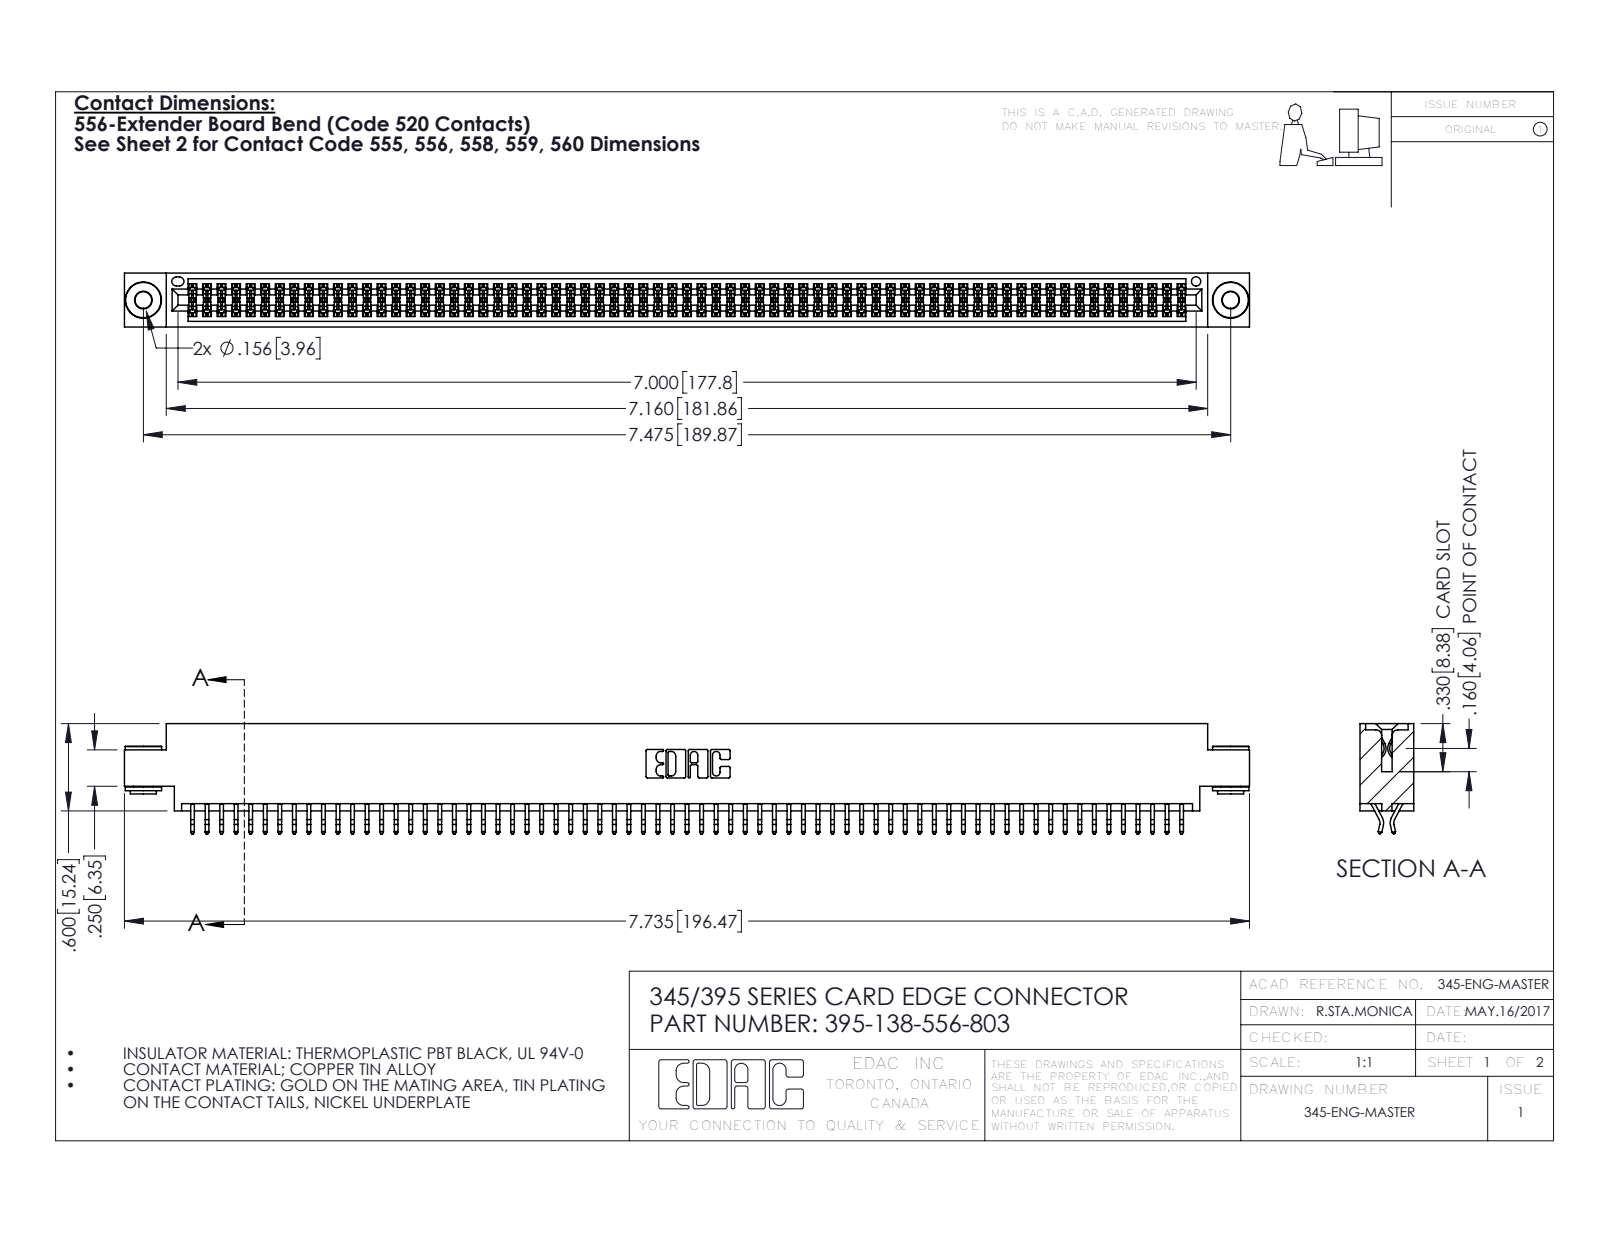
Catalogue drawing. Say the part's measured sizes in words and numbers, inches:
The part is named "395-138-556-803; 345-292-001_556 Tail; 345 Part_0.170 Offset - 0.156 Dia-TH; 345-250-002_345-250-002-102". Its 3-D file was written by "SolidWorks 2016 (CONFIG_CONTROL_DESIGN)". It is 141 solids with 7896 faces: 5200 planar, 2688 cylindrical and 8 other. Overall it measures 7.735 by 0.757 by 0.37 inches. Its volume is 1.174 cubic inches and its surface area 45.24 square inches. Round holes: 2 of diameter 0.116, 2 of diameter 0.156, 1 of diameter 0.064. Round bosses or shafts: 2 of diameter 0.25, 2 of diameter 0.18, 2 of diameter 0.136. Partial cylindrical surfaces (rounded edges, fillets, slot ends): 207 of radius 0.006, 22 of radius 0.01, 6 of radius 0.007, 6 of radius 0.031, 3 of radius 0.026, 2 of radius 0.01, 2 of radius 0.014, 2 of radius 0.019. The main face-to-face distances are 0.072, 0.298, 0.37, 0.2, 0.025, 0.098, 0.272, 0.225, 0.175, 0.149. The hole center spacings are 0.27, 7.239, 7.475.
